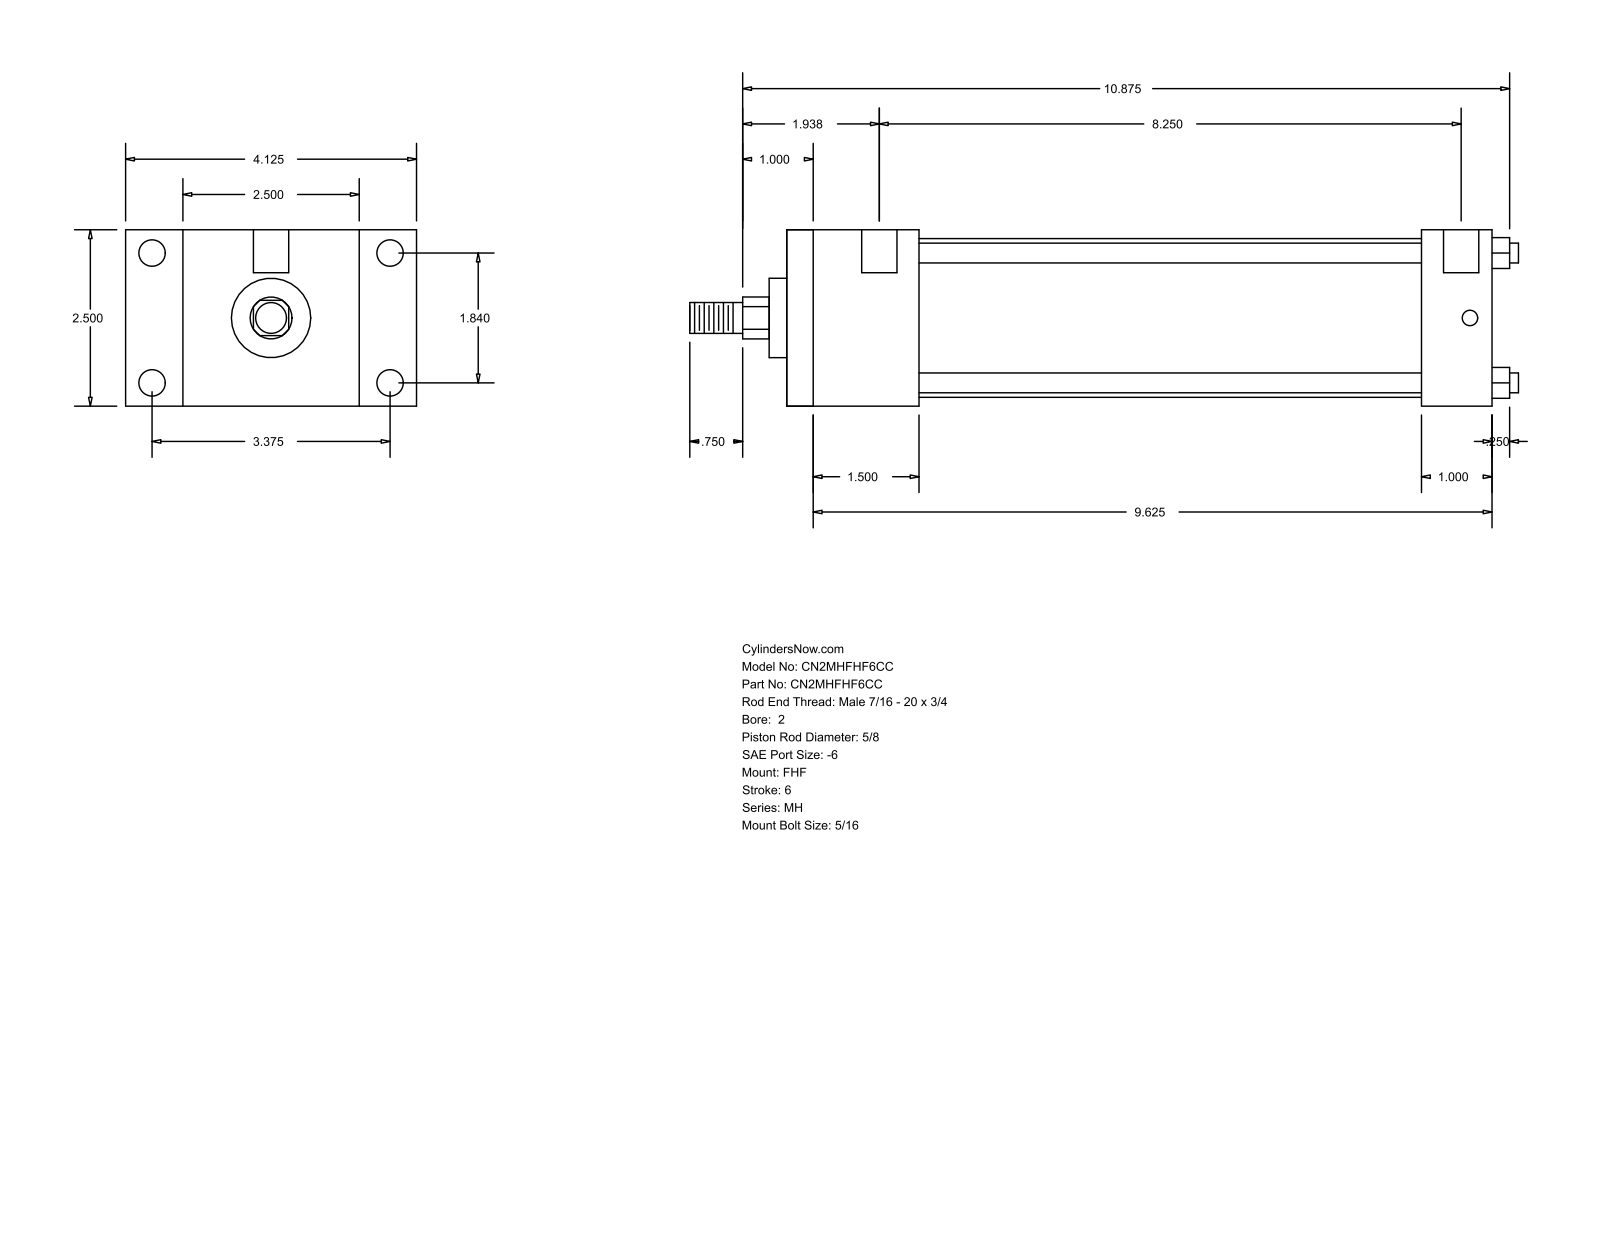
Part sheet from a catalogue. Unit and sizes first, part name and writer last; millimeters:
Units: millimetres
Overall size (bounding box): 298.45 × 104.78 × 63.5
Round holes (diameter × count): ⌀5.56 ×4, ⌀9.53 ×4, ⌀12.7 ×2
Round bosses / shafts (diameter × count): ⌀7.14 ×4, ⌀57.15 ×1, ⌀28.57 ×1, ⌀15.88 ×1, ⌀11.11 ×1
Partial cylindrical surfaces — rounded edges, fillets, slot ends (radius × count): R7.54 ×1
Main face-to-face distances: 63.5, 47.62, 254, 206.38, 20.64, 84.14, 104.78, 228.59, 180.97, 25.41
Hole centre spacings: 46.74, 85.72, 97.63, 217.49, 3.18, 4.76, 209.55, 212.73
Bodies: 0 solids, 88 faces (60 planar, 28 cylindrical, 0 other)
Part name (STEP PRODUCT): MH_FHF__0200_0.625
STEP written by: GSSL Pune (CONFIG_CONTROL_DESIGN)
